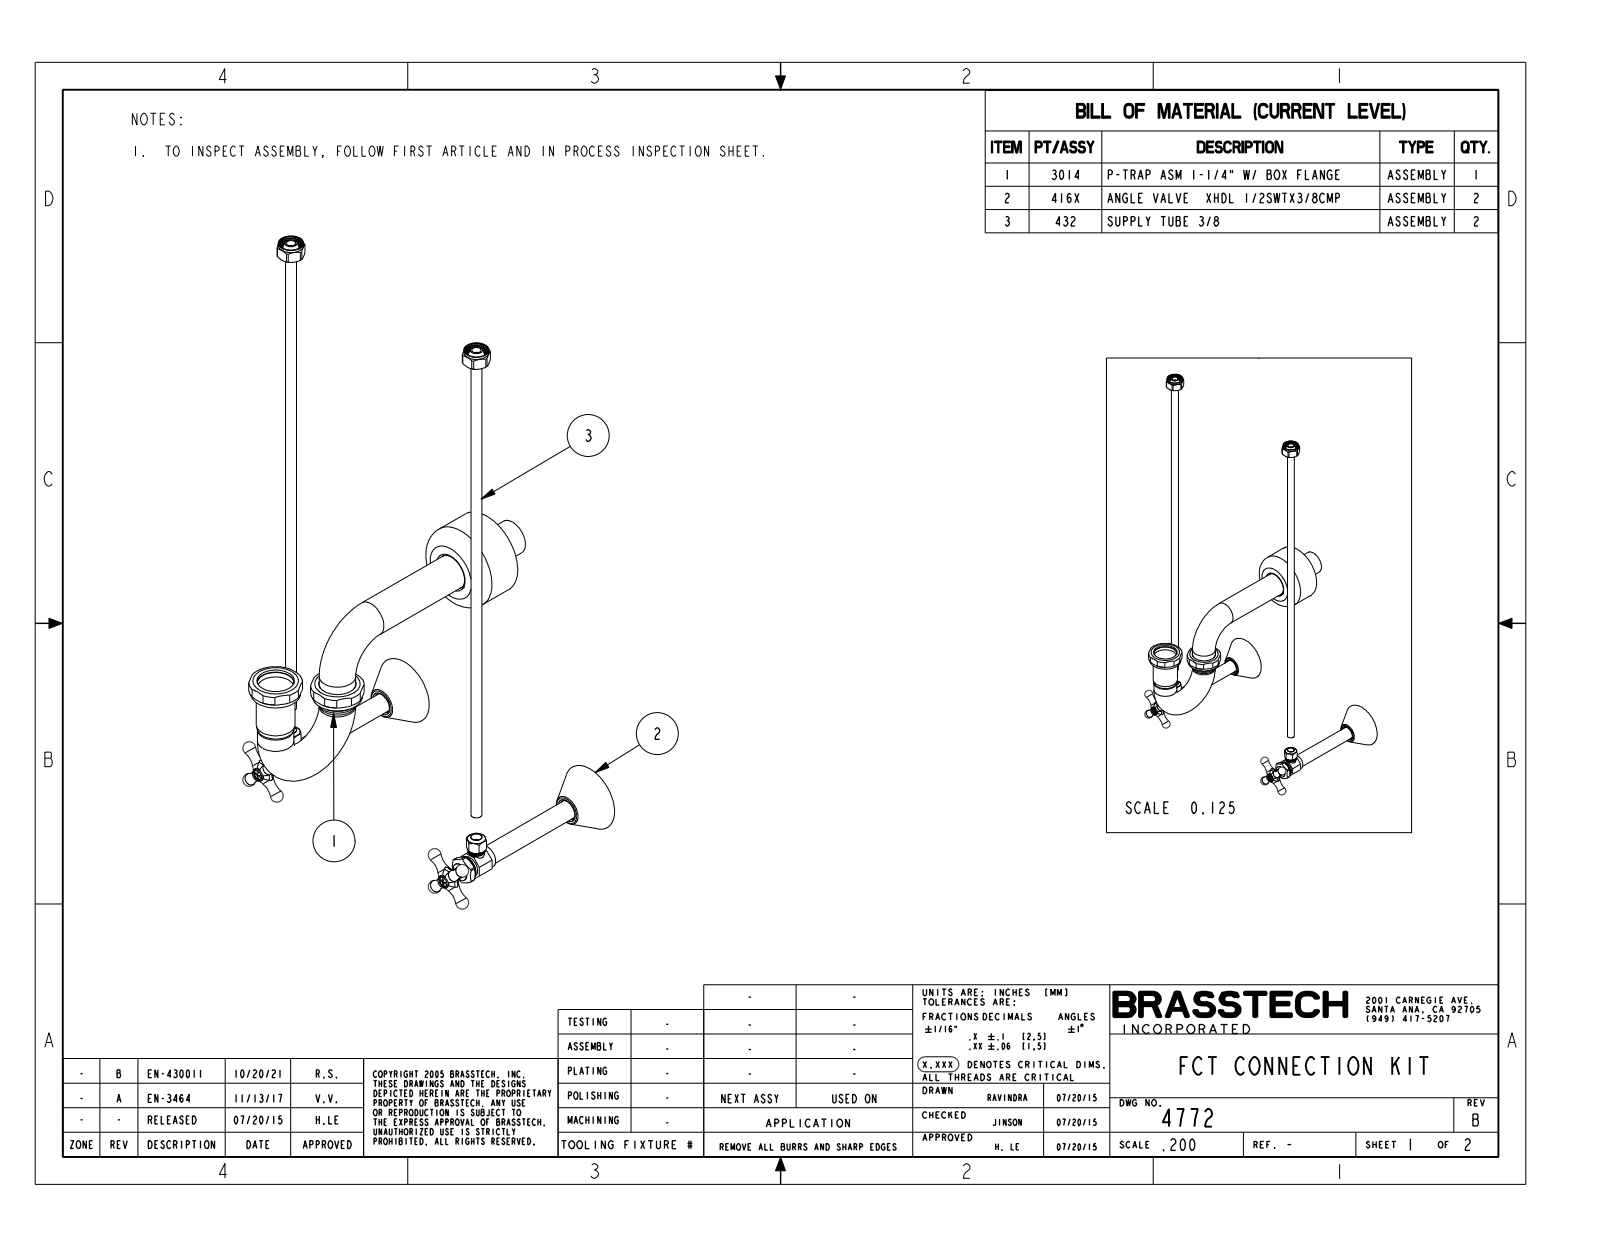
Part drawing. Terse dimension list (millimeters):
name: 50319; 50320; 91193; 50321 (+8 more)
written by: CREO PARAMETRIC BY PTC INC, 2018400 (AUTOMOTIVE_DESIGN)
unit: mm
bodies: 37 solids, 1720 faces (514 planar, 643 cylindrical, 563 other)
size: 536.3 × 314.5 × 289.6
volume: 149 700 mm³; area: 275 400 mm²
holes: 2× ⌀3.3, 2× ⌀4.4, 2× ⌀4.9, 2× ⌀7.6, 2× ⌀8.1, 2× ⌀8.4, 2× ⌀9.6, 2× ⌀9.6, 2× ⌀9.7, 2× ⌀9.7, 2× ⌀9.9, 2× ⌀10
bosses: 2× ⌀43.3, 2× ⌀38.1, 2× ⌀31.8, 2× ⌀22, 2× ⌀21.8, 2× ⌀20.7, 2× ⌀20.3, 2× ⌀19.1
rounds: 36× R0.3, 12× R1.3, 12× R1.8, 2× R4.3, 2× R4.7, 2× R4.7, 2× R12.4, 2× R23.4
face distances: 41.3, 22.9, 4.8, 0.6, 15.9, 114.3, 111.8, 111.3, 228.6, 3.3
hole spacings: 228.6, 32.8, 231, 76.2, 102.3, 110.8, 127.5, 134.2
